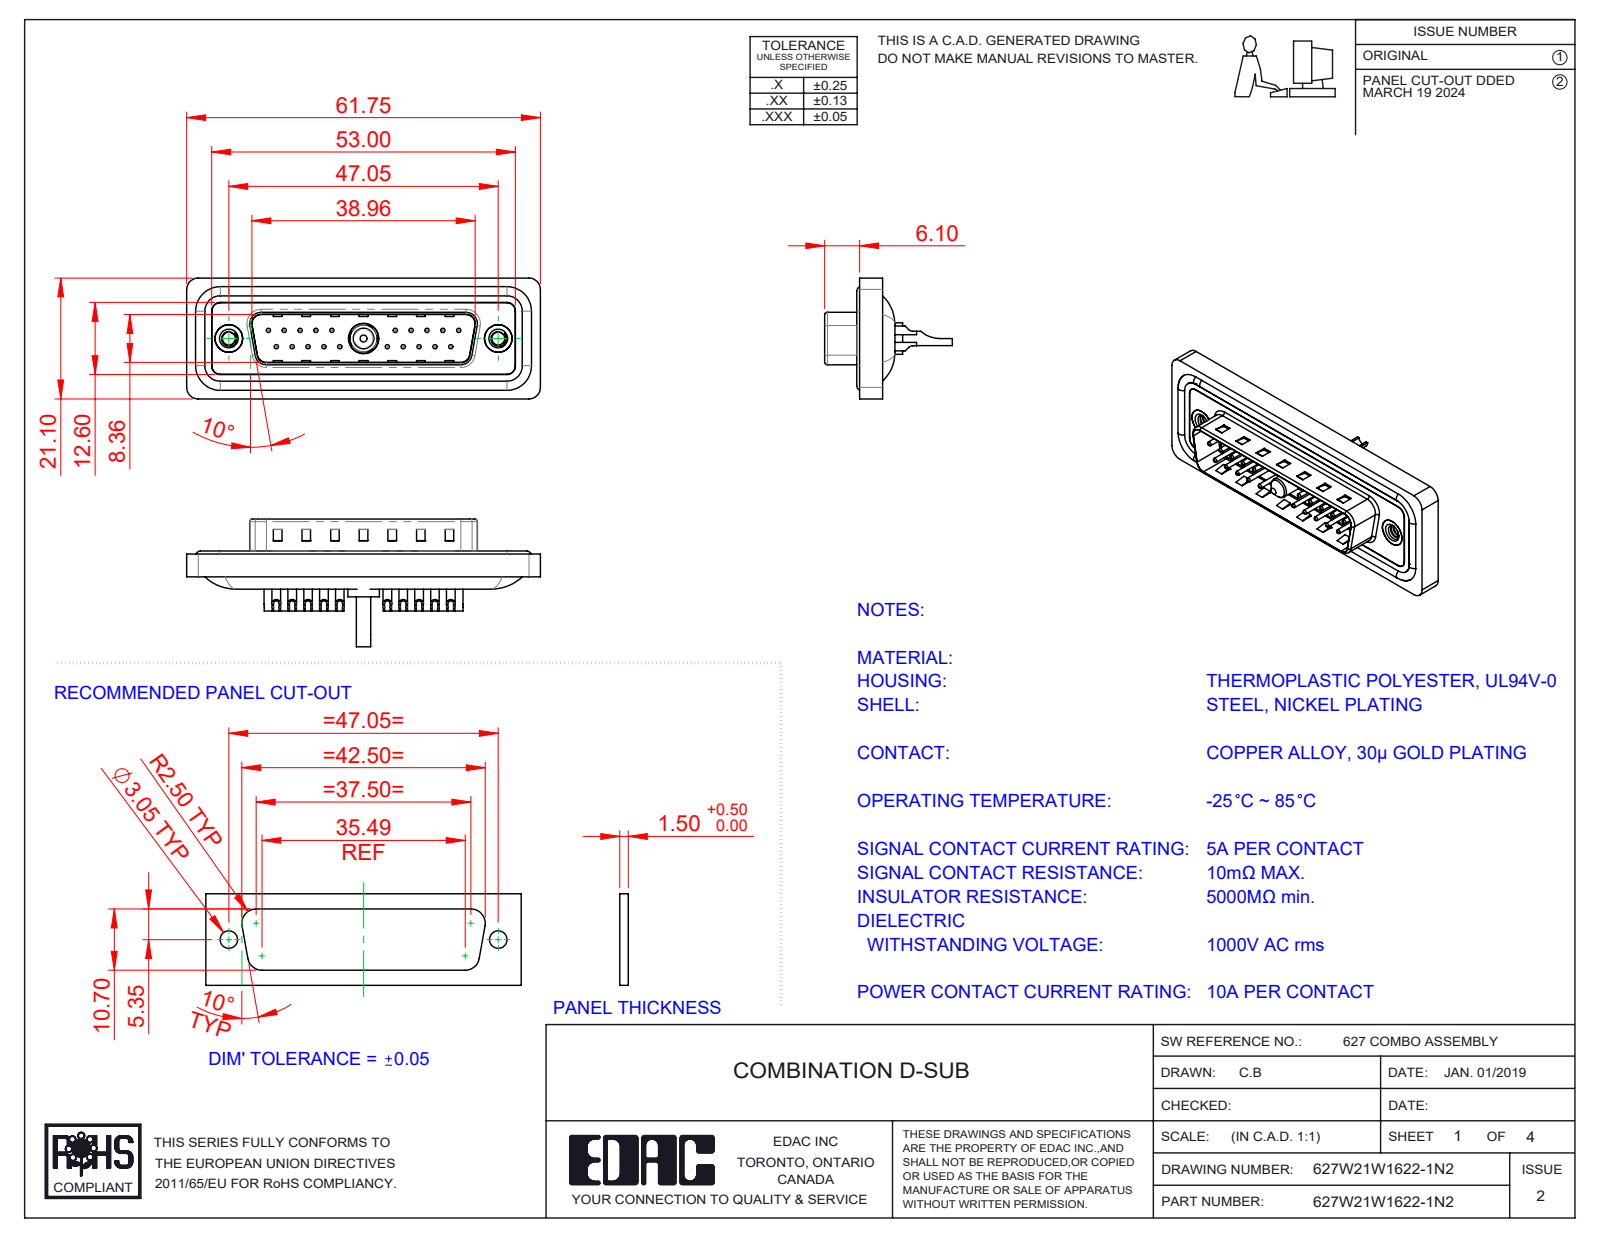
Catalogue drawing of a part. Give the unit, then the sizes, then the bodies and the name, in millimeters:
Units: millimetres
Overall size (bounding box): 61.75 × 22.3 × 21.1
Round holes (diameter × count): ⌀0.75 ×20, ⌀1 ×20, ⌀1.6 ×20, ⌀2 ×20, ⌀2.26 ×2, ⌀4 ×2, ⌀4.8 ×2, ⌀5 ×2, ⌀1.7 ×1, ⌀4.85 ×1, ⌀5.3 ×1
Round bosses / shafts (diameter × count): ⌀1.5 ×20, ⌀1.6 ×4, ⌀4.9 ×2, ⌀5.5 ×1, ⌀5.2 ×1, ⌀4.75 ×1, ⌀3.75 ×1, ⌀3.6 ×1
Partial cylindrical surfaces — rounded edges, fillets, slot ends (radius × count): R1.5 ×22, R2 ×18, R0.5 ×8, R1.6 ×8, R1 ×6, R0.25 ×4, R0.6 ×4, R0.65 ×4
Main face-to-face distances: 0.4, 1.5, 1.1, 1.6, 0.5, 3.1, 2.9, 4.1, 0.82, 9.58
Hole centre spacings: 3.16, 2.77, 5.54, 8.31, 5.04, 19.39, 20.97, 22.16
Volume: 7 226 mm³ · Surface area: 12 160 mm²
Bodies: 29 solids, 1268 faces (401 planar, 530 cylindrical, 337 other)
Part name (STEP PRODUCT): 627Combo Housing_21W1; 627Combo Contact Row 1_22; Power Pin_10A SC; 627Combo Contact Row 2_22 (+5 more)
STEP written by: SolidWorks 2023 (CONFIG_CONTROL_DESIGN)
